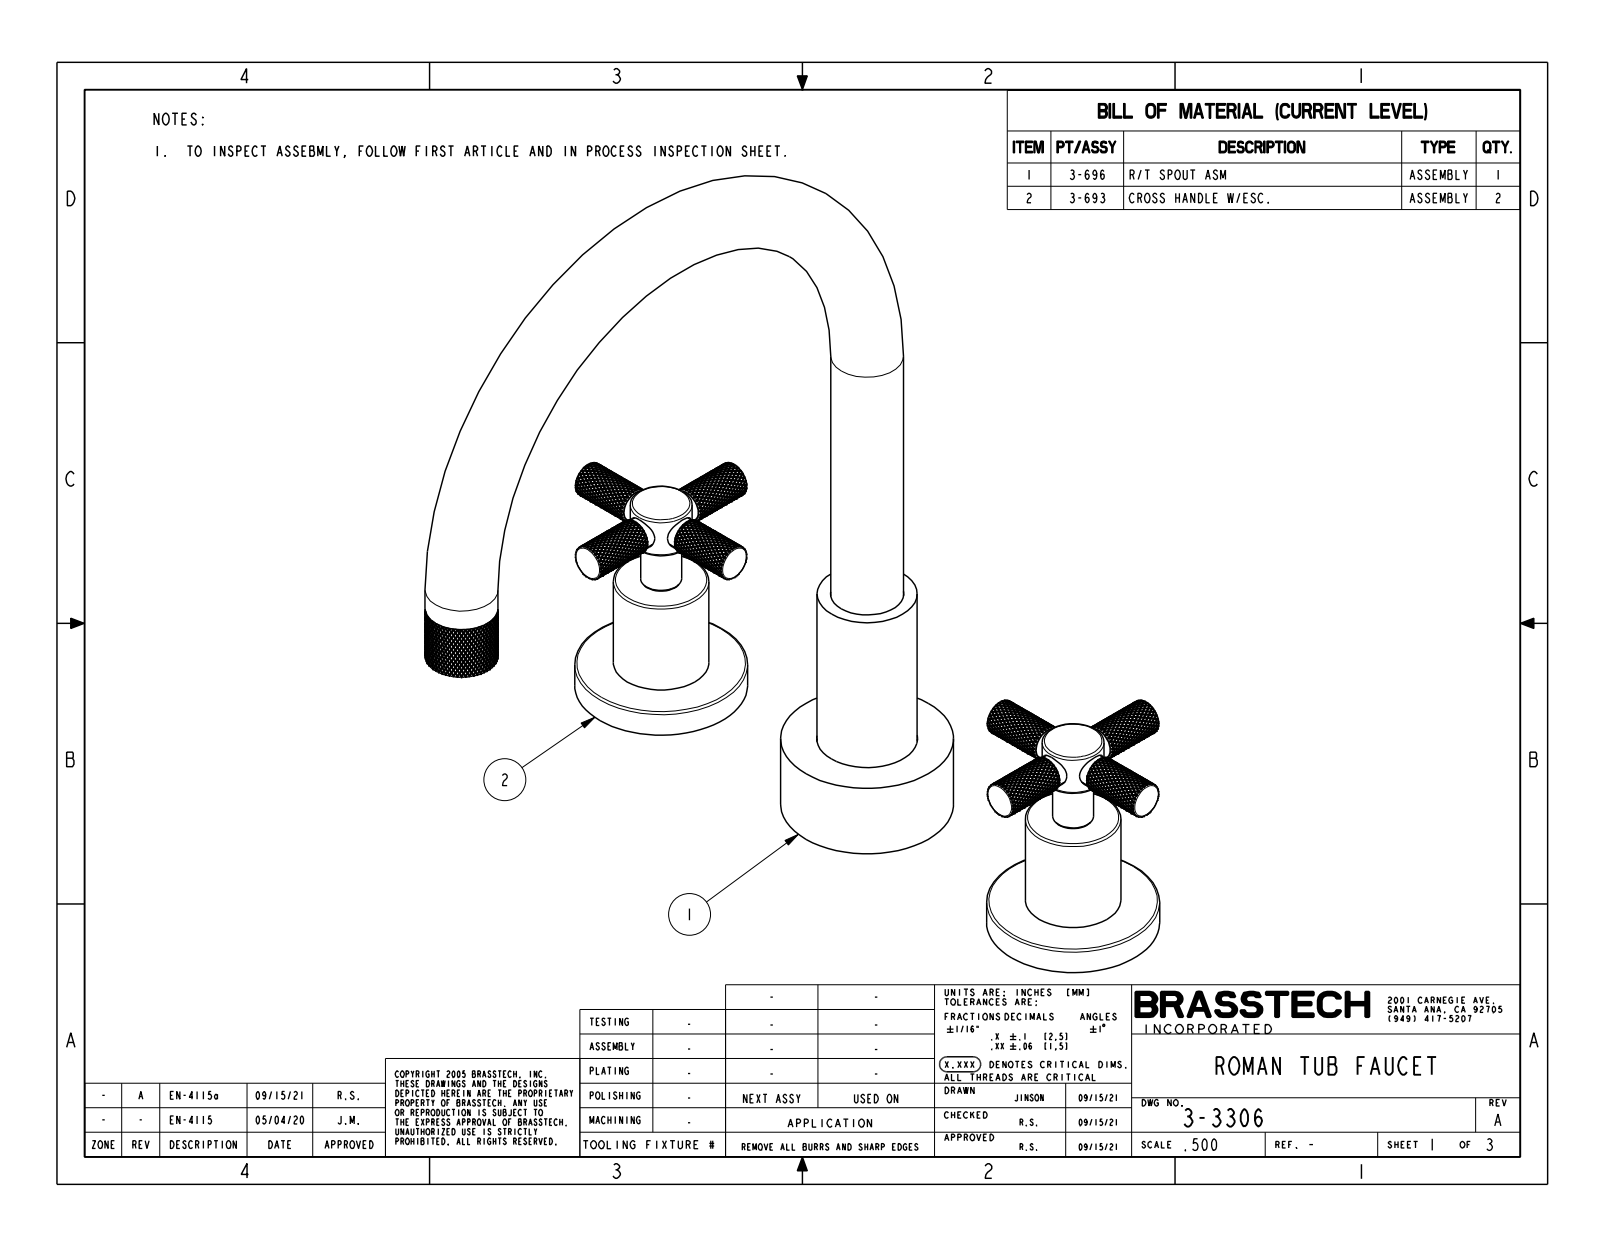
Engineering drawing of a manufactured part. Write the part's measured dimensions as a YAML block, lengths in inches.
part_name: "3-3306"
step_written_by: "CREO PARAMETRIC BY PTC INC, 2018400 (CONFIG_CONTROL_DESIGN)"
units: inches
bodies: {solids: 3, faces: 27570, planar: 217, cylindrical: 5318, other: 22035}
overall_size: [11.978, 10.85, 9.8]
volume: 31.57
surface_area: 152.6
round_holes:
  - {diameter: 0.465, count: 3}
  - {diameter: 0.56, count: 1}
  - {diameter: 0.61, count: 1}
  - {diameter: 0.792, count: 1}
  - {diameter: 0.826, count: 1}
  - {diameter: 0.871, count: 1}
  - {diameter: 0.9, count: 1}
  - {diameter: 1.385, count: 1}
round_bosses_or_shafts:
  - {diameter: 2.375, count: 3}
  - {diameter: 0.5, count: 3}
  - {diameter: 0.44, count: 3}
  - {diameter: 1.313, count: 2}
  - {diameter: 1.25, count: 2}
  - {diameter: 1, count: 2}
  - {diameter: 0.85, count: 2}
  - {diameter: 0.563, count: 2}
partial_cylinders:
  - {radius: 0.332, count: 1}
face_to_face_distances: [0.375, 1.103, 0.728, 1.775, 1.4, 0.672, 3.066, 2.691, 1.963, 1.291]
hole_center_spacings: [7.875, 8]
